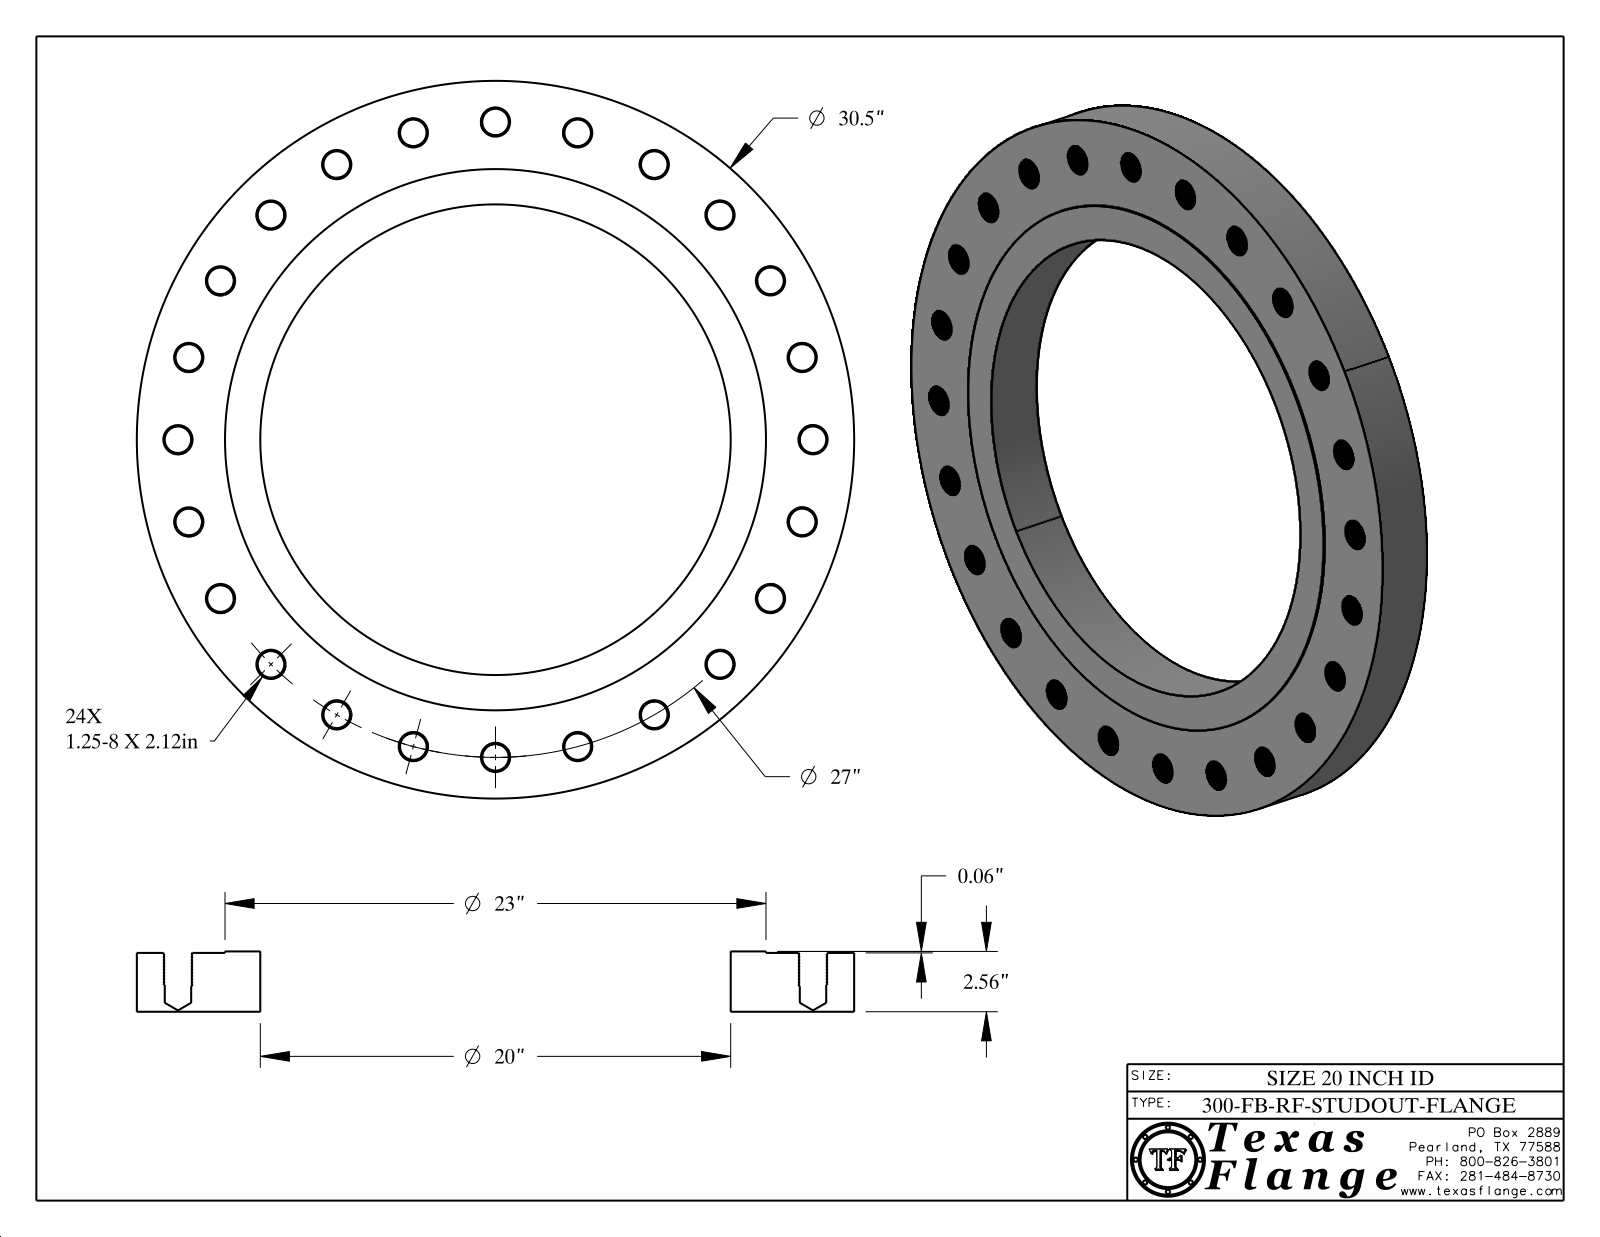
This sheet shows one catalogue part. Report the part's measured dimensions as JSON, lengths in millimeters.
{"part_name": "20-300-FB-RF-STUDOUT-FLANGE", "step_written_by": "CATIA V5 STEP AP214 (AUTOMOTIVE_DESIGN)", "units": "millimeters", "bodies": {"solids": 1, "faces": 2266, "planar": 368, "cylindrical": 602, "other": 1296}, "overall_size": [774.7, 774.7, 65.1], "volume_mm3": 16230000, "surface_area_mm2": 951600, "round_holes": [[28.6, 24], [25.4, 1], [508, 1]], "round_bosses_or_shafts": [[1.5, 8], [774.7, 1], [584.2, 1], [20, 1]], "face_to_face_distances": [63.5, 1.6, 65.1, 64.7, 63.1, 0.4, 7.6, 7.4, 1.4, 6.3], "hole_center_spacings": [342.9, 89.5, 177.5, 262.5, 417.5, 633.6, 679.9, 544.1]}
